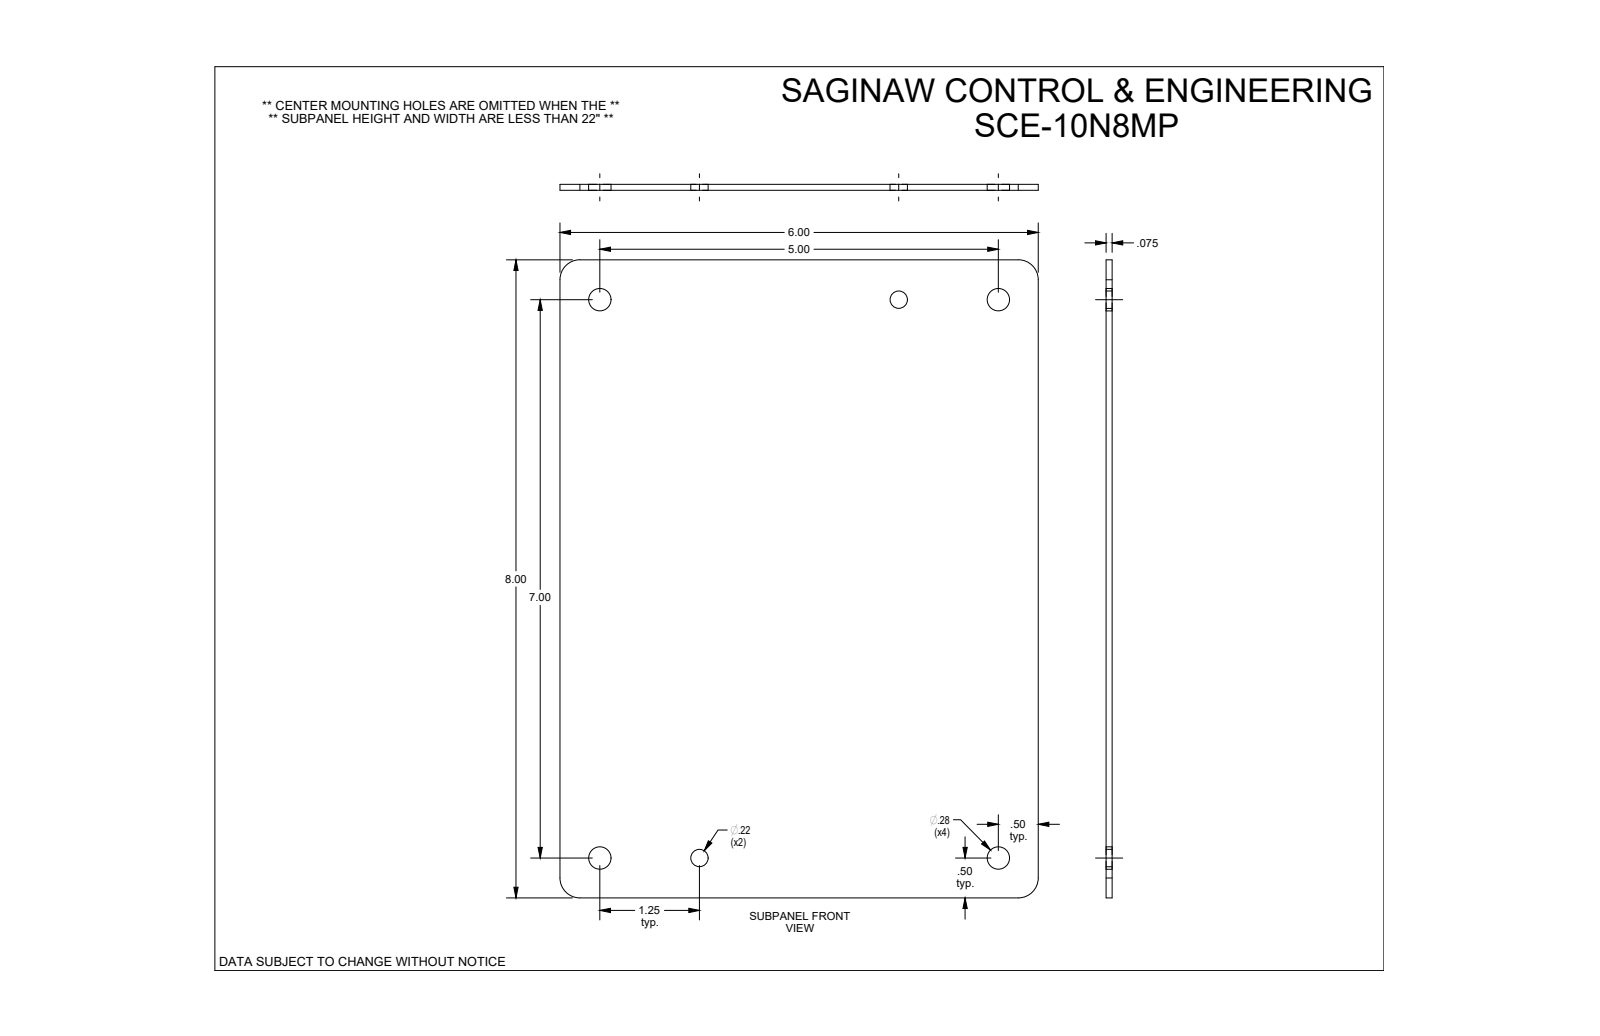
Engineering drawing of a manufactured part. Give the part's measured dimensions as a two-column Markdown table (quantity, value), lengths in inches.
| quantity | value |
| --- | --- |
| part name | SCE-10N8MP |
| STEP written by | SolidWorks 2019 (CONFIG_CONTROL_DESIGN) |
| units | inches |
| bodies | 1 solid, 16 faces (6 planar, 10 cylindrical, 0 other) |
| overall size | 8 × 6 × 0.075 |
| volume | 3.572 in³ |
| surface area | 97.68 in² |
| round holes (diameter × count) | 0.281 × 4, 0.218 × 2 |
| partial cylindrical surfaces (radius × count) | 0.25 × 4 |
| main face-to-face distances | 0.075, 6, 8 |
| hole center spacings | 1.25, 3.75, 5, 7, 7.111, 7.941, 8.602, 7.433 |
